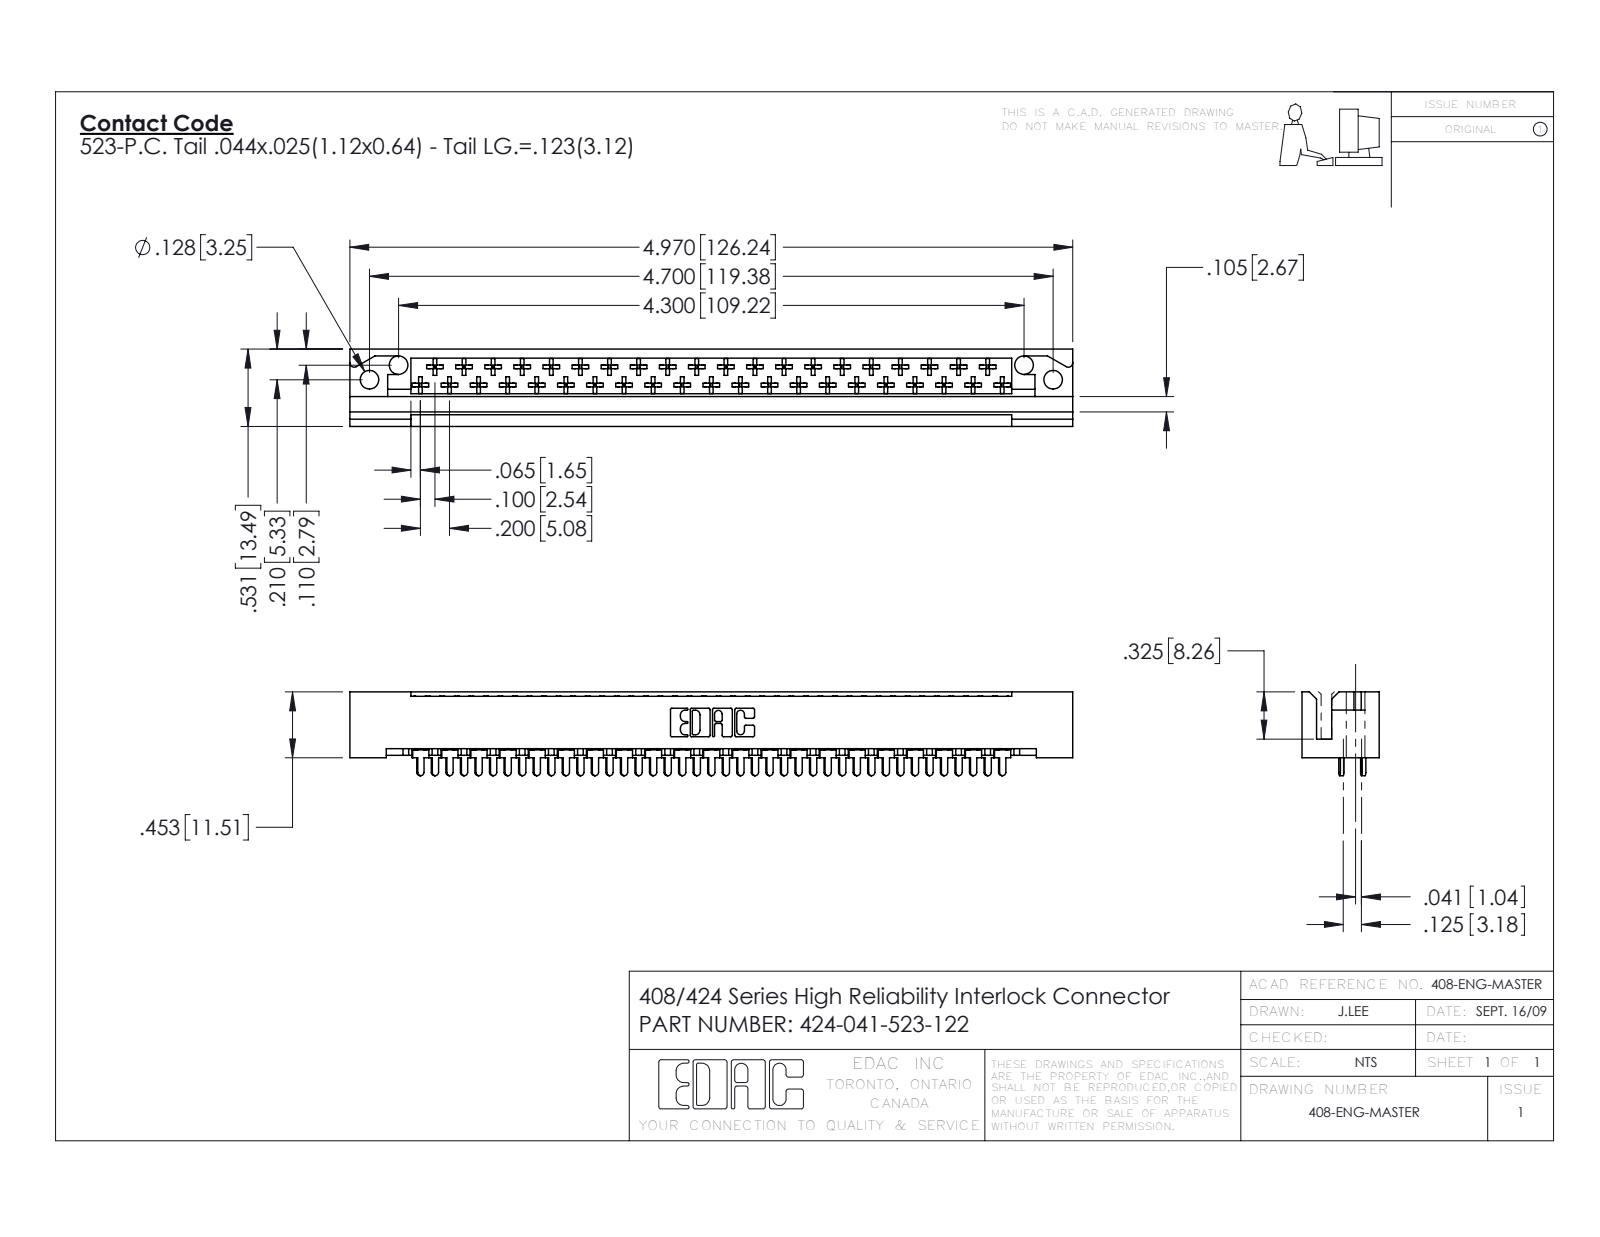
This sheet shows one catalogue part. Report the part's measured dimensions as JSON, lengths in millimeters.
{"part_name": "408-290-001_408-290-123 - Top; 424-041-523-122; 424 Part_041; 408-290-001_408-290-123 - Bottom", "step_written_by": "SolidWorks 2016 (CONFIG_CONTROL_DESIGN)", "units": "millimeters", "bodies": {"solids": 42, "faces": 2400, "planar": 1811, "cylindrical": 425, "other": 164}, "overall_size": [126.2, 14.6, 13.5], "volume_mm3": 13000, "surface_area_mm2": 17110, "round_holes": [[3.3, 4]], "partial_cylinders_radius": [[0.3, 246], [0.5, 43], [0.6, 41], [0.3, 22], [0.2, 6], [0.8, 6], [0.7, 3], [0.8, 2]], "face_to_face_distances": [2.5, 7.5, 0.6, 13.5, 3.2, 6.9, 6, 6.6, 0.6, 5.5], "hole_center_spacings": [5.7, 114.3, 109.2, 119.4]}
